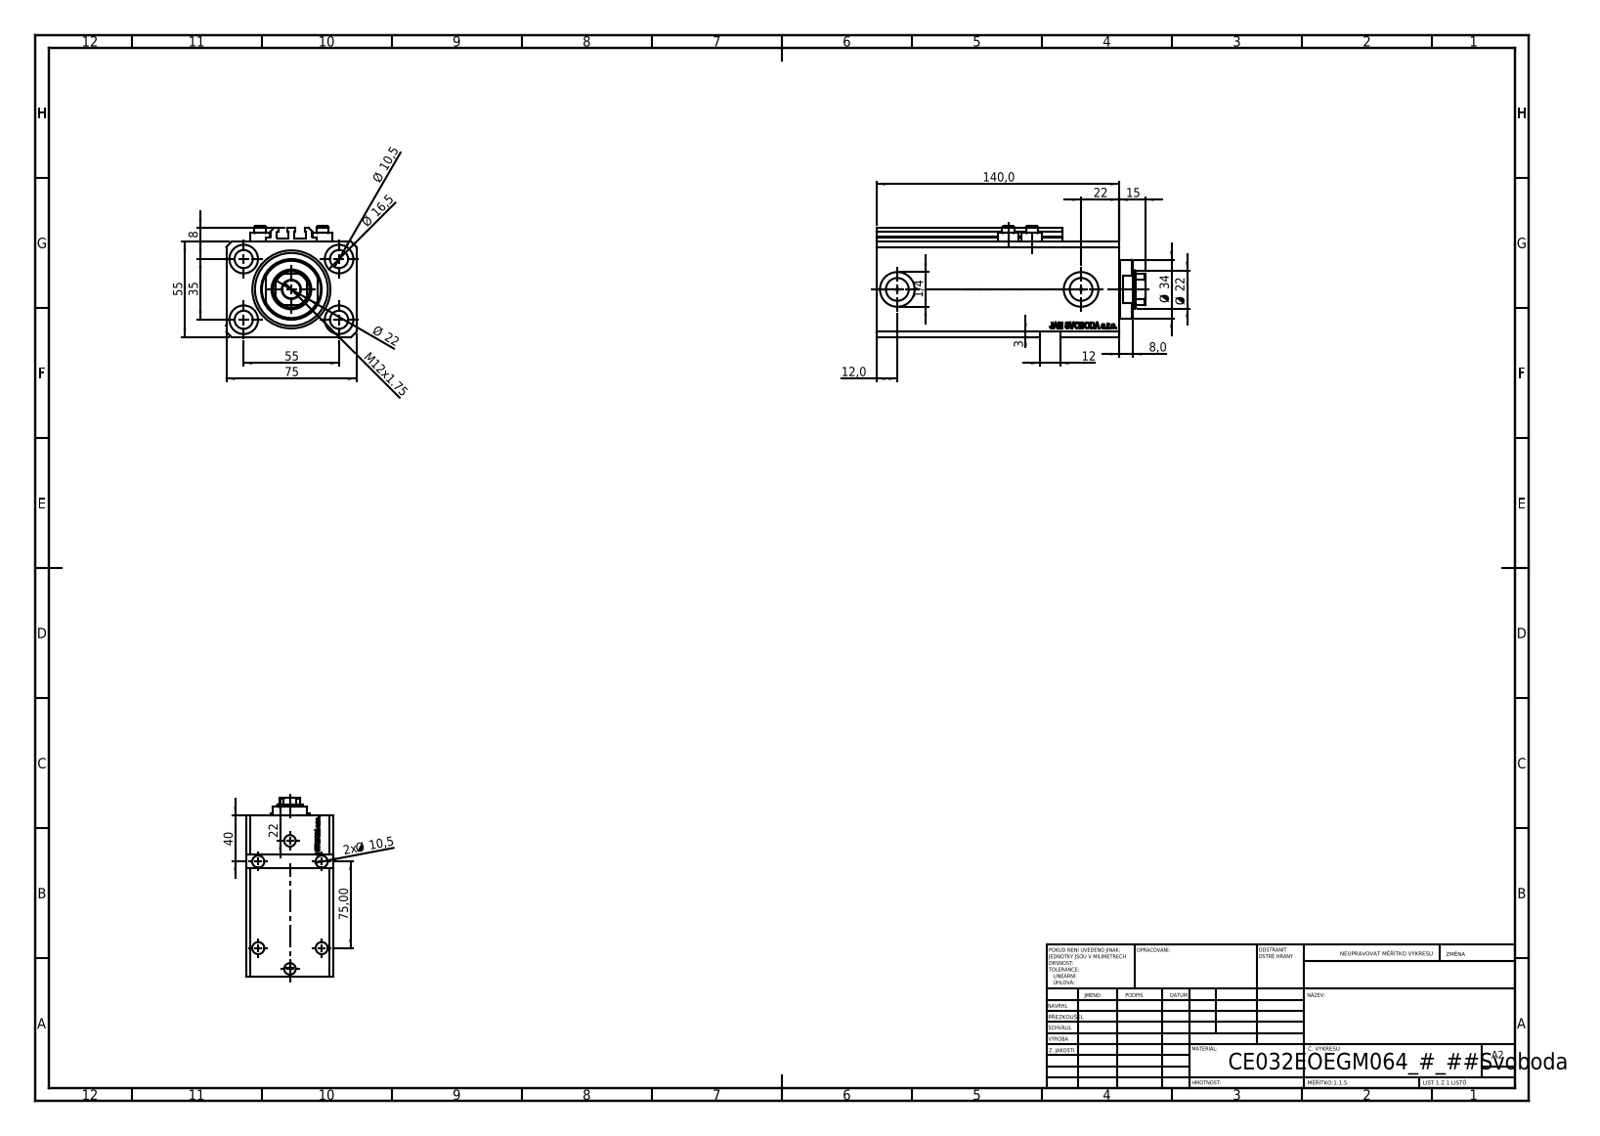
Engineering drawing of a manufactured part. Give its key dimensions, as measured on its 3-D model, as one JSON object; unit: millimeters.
{"part_name": "V250CE_C_VCP; ALLEN BOLT V250CE; V250CE_E_Body; V250CE_VC_E", "step_written_by": "SolidWorks 2019 (CONFIG_CONTROL_DESIGN)", "units": "millimeters", "bodies": {"solids": 8, "faces": 1084, "planar": 514, "cylindrical": 146, "other": 424}, "overall_size": [155, 75, 64], "volume_mm3": 485219, "surface_area_mm2": 115303, "round_holes": [[10.5, 9], [1.25, 4], [4, 4], [16.5, 4], [10, 2], [13.16, 2], [20, 2], [22, 1], [32, 1], [45, 1]], "round_bosses_or_shafts": [[11.6, 4], [7, 4], [34, 1]], "partial_cylinders_radius": [[0.2, 10], [10.5, 1]], "face_to_face_distances": [55, 75, 15, 140, 125, 3, 9.9, 57, 115.1, 130.1], "hole_center_spacings": [32.6, 32.87, 55, 96.98, 13.6, 14.09, 25.81, 32.58]}
